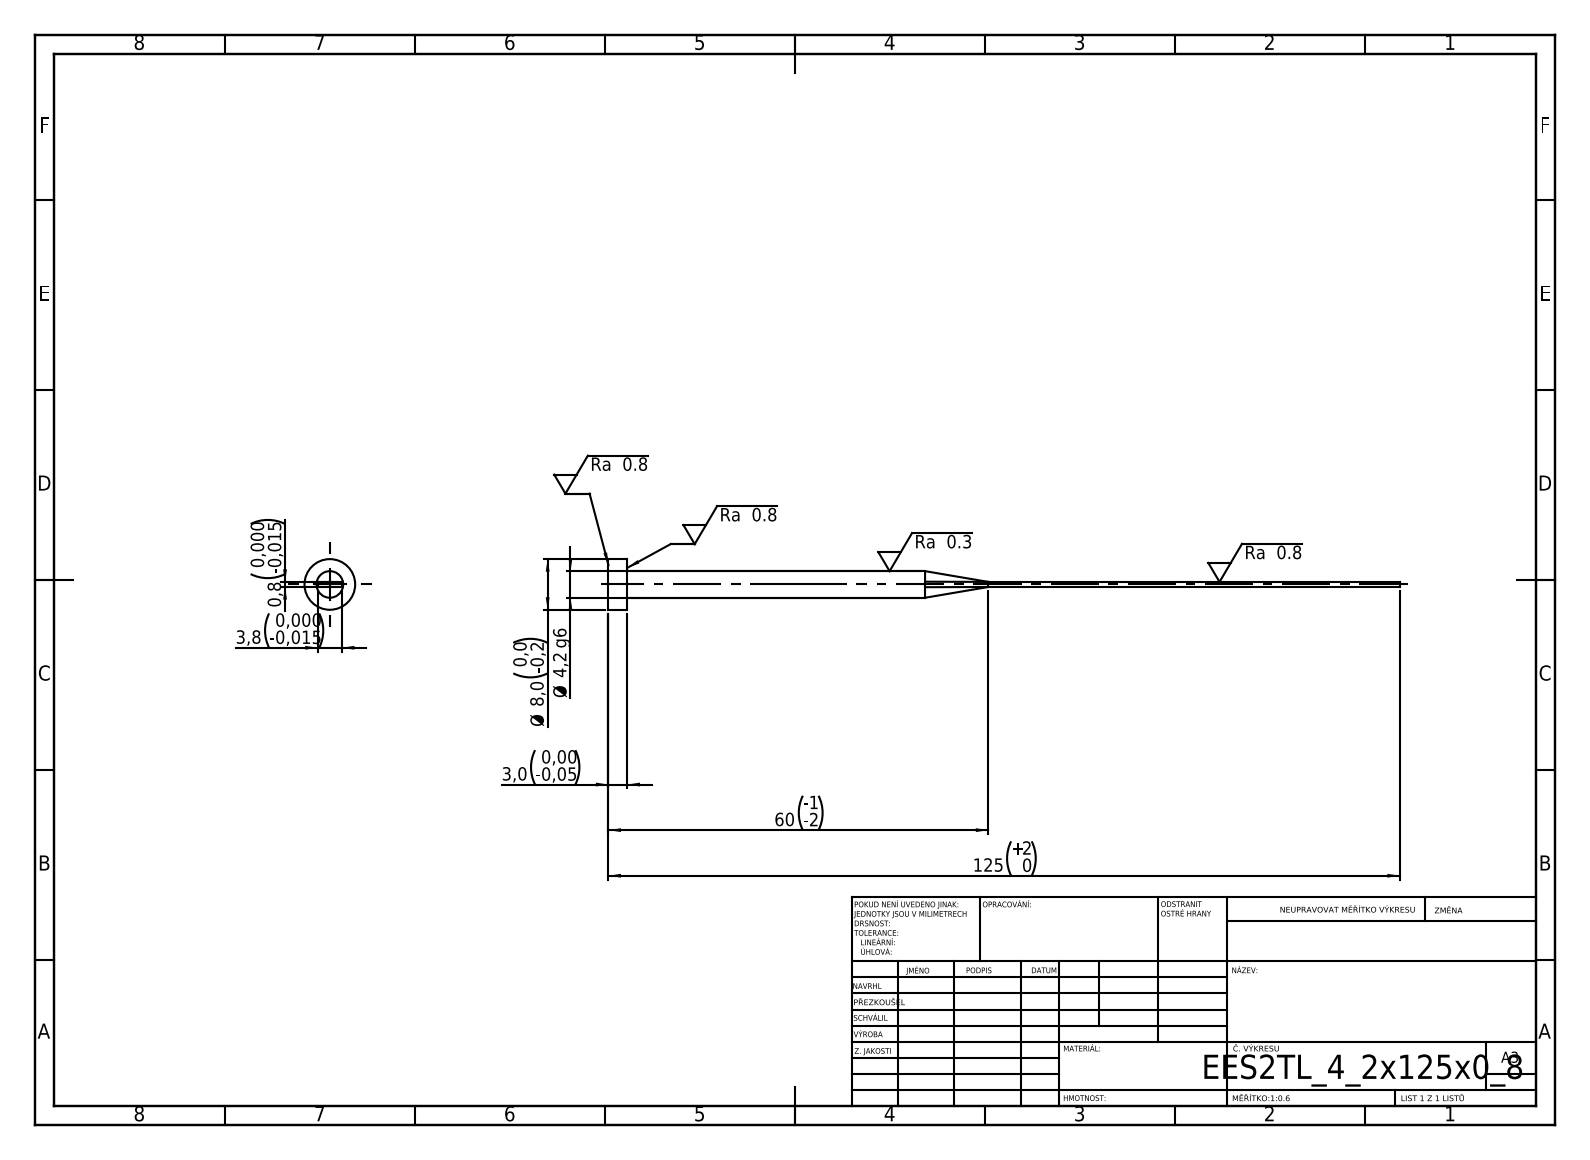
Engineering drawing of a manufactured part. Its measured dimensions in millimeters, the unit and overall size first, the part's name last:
Units: millimetres
Overall size (bounding box): 125 × 8 × 8
Round bosses / shafts (diameter × count): ⌀8 ×1, ⌀4.2 ×1
Main face-to-face distances: 0.8, 3.8, 3, 125, 122
Volume: 1 080 mm³ · Surface area: 1 491 mm²
Bodies: 1 solid, 15 faces (7 planar, 4 cylindrical, 4 other)
STEP written by: SolidWorks 2019 (CONFIG_CONTROL_DESIGN)
